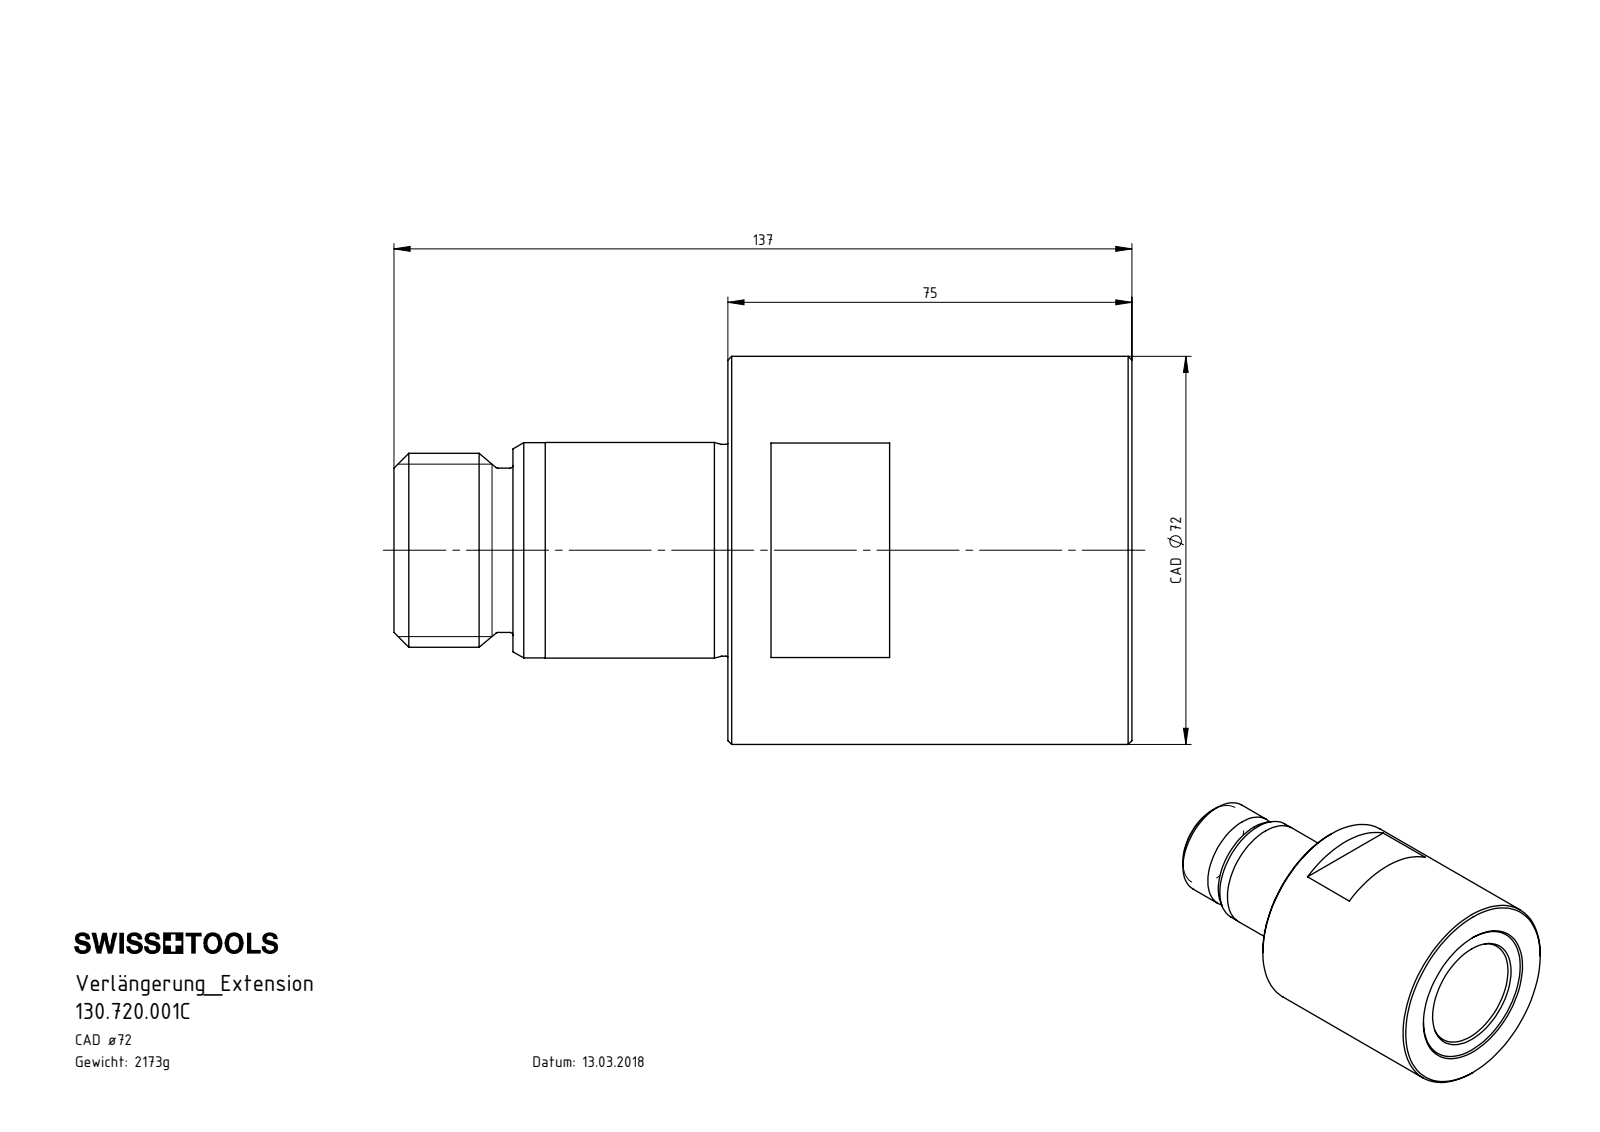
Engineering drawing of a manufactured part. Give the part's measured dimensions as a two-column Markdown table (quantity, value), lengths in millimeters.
| quantity | value |
| --- | --- |
| part name | 130.720.001C |
| STEP written by | SolidWorks 2017 (CONFIG_CONTROL_DESIGN) |
| units | millimeters |
| bodies | 1 solid, 71 faces (13 planar, 20 cylindrical, 38 other) |
| overall size | 137 × 72 × 72 |
| volume | 276 810 mm³ |
| surface area | 43 516 mm² |
| round holes (diameter × count) | 8.5 × 1, 32 × 1, 40 × 1, 40.6 × 1 |
| round bosses / shafts (diameter × count) | 72 × 1, 39.95 × 1, 39.3 × 1, 36 × 1, 30.5 × 1 |
| main face-to-face distances | 75, 60, 74.4, 0.6, 62, 136.4, 137, 22.1, 39.9, 114.3 |
